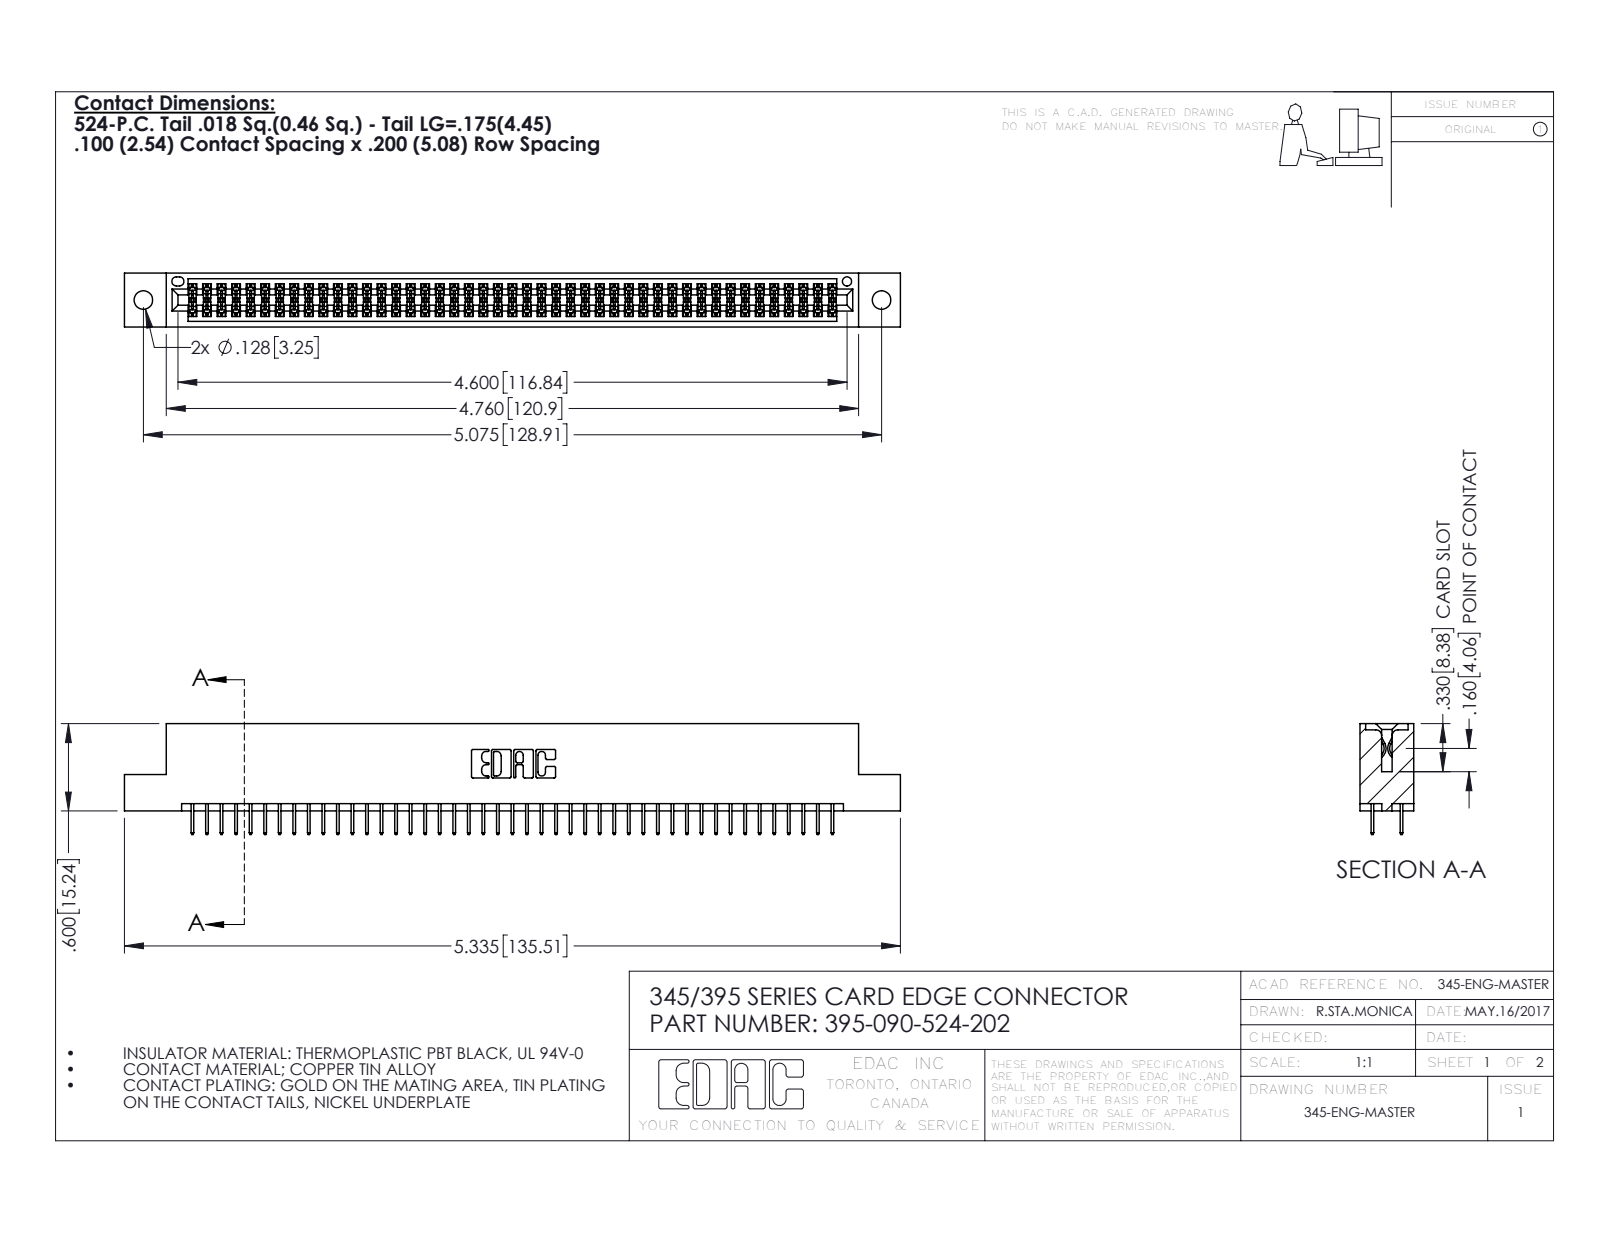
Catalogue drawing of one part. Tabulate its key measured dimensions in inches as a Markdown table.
| quantity | value |
| --- | --- |
| part name | 395-090-524-202; 345 Part_Flush Mounting Lugs - 0.128 Dia; 345-292-001_345-293-124 |
| STEP written by | SolidWorks 2016 (CONFIG_CONTROL_DESIGN) |
| units | inches |
| bodies | 91 solids, 4986 faces (3590 planar, 1396 cylindrical, 0 other) |
| overall size | 5.335 × 0.762 × 0.37 |
| volume | 0.794 in³ |
| surface area | 28.94 in² |
| round holes (diameter × count) | 0.128 × 2, 0.064 × 1 |
| partial cylindrical surfaces (radius × count) | 0.006 × 135, 0.01 × 22, 0.007 × 6, 0.031 × 6, 0.026 × 3, 0.014 × 2, 0.019 × 2, 0.022 × 2 |
| main face-to-face distances | 0.298, 0.072, 0.2, 0.37, 0.098, 0.272, 0.025, 0.225, 0.072, 0.175 |
| hole center spacings | 0.27, 4.839, 5.075 |
